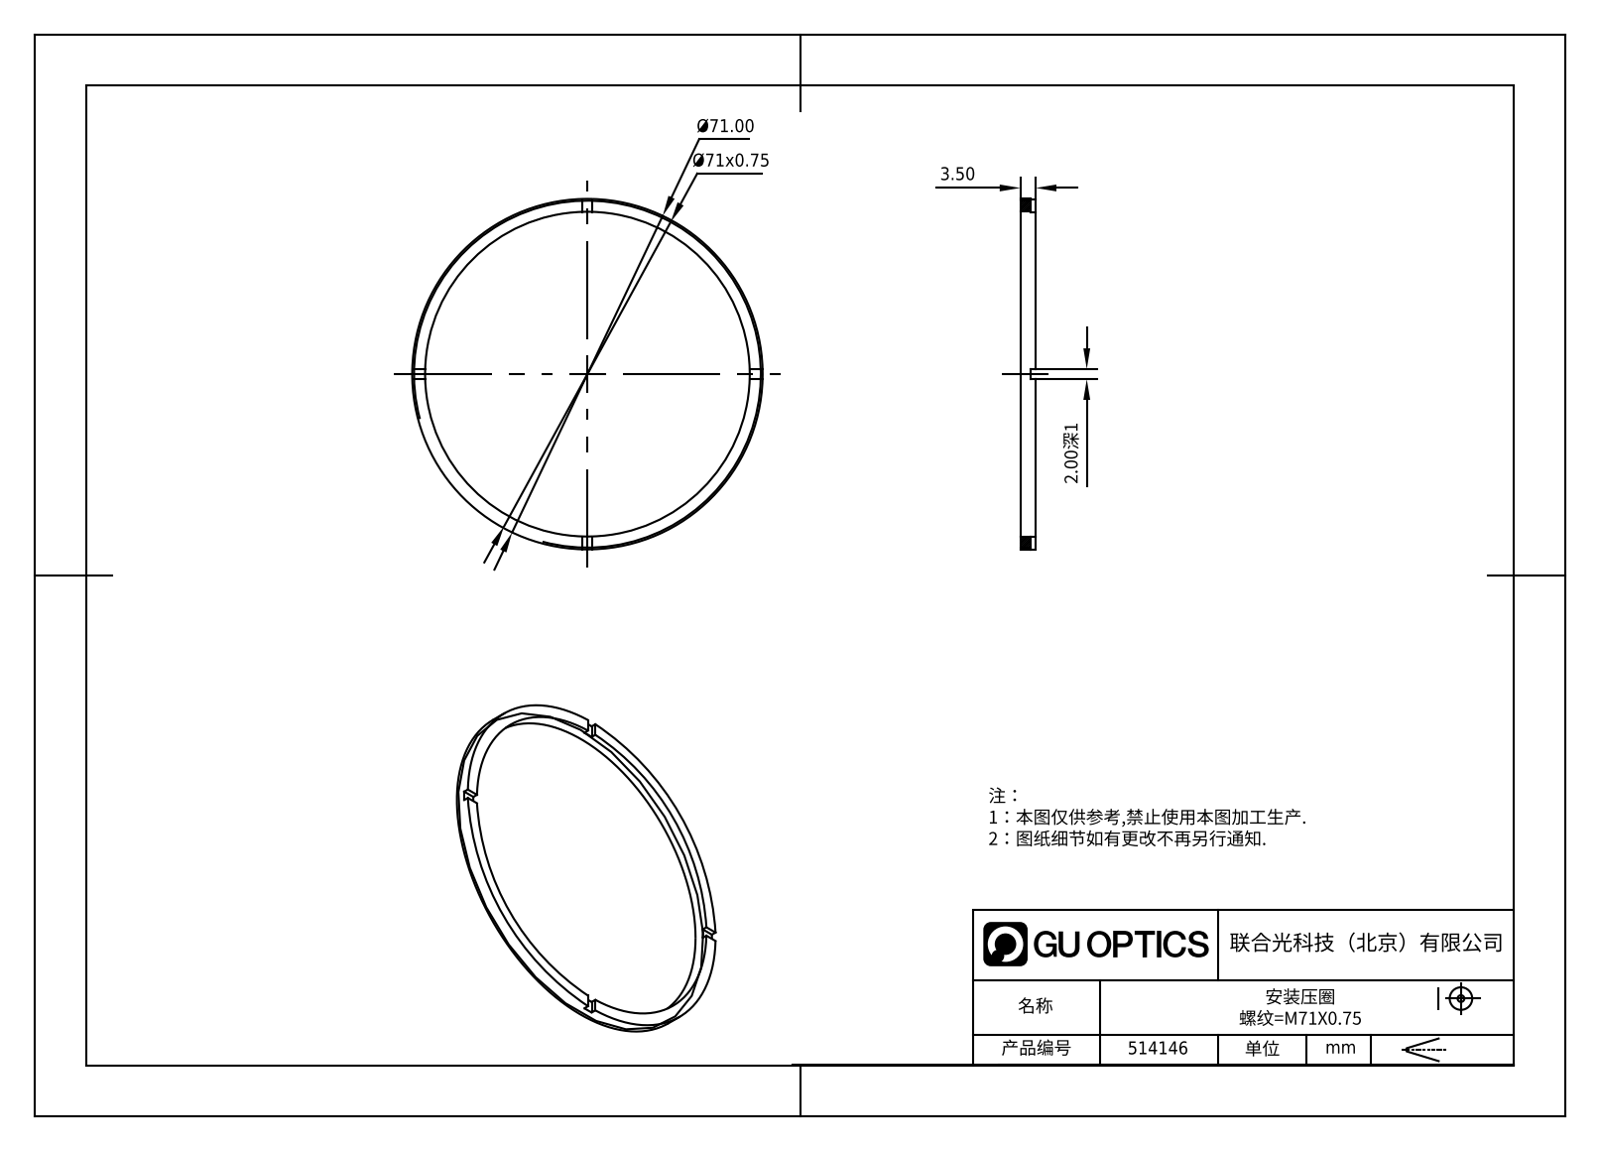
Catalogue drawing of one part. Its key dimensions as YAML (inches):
part_name: "514146"
step_written_by: "SolidWorks 2020 (CONFIG_CONTROL_DESIGN)"
units: inches
bodies: {solids: 1, faces: 21, planar: 17, cylindrical: 4, other: 0}
overall_size: [2.795, 2.795, 0.138]
volume: 0.135
surface_area: 4.317
round_holes:
  - {diameter: 2.559, count: 1}
round_bosses_or_shafts:
  - {diameter: 2.795, count: 1}
face_to_face_distances: [0.138, 0.098, 0.039, 0.079]
